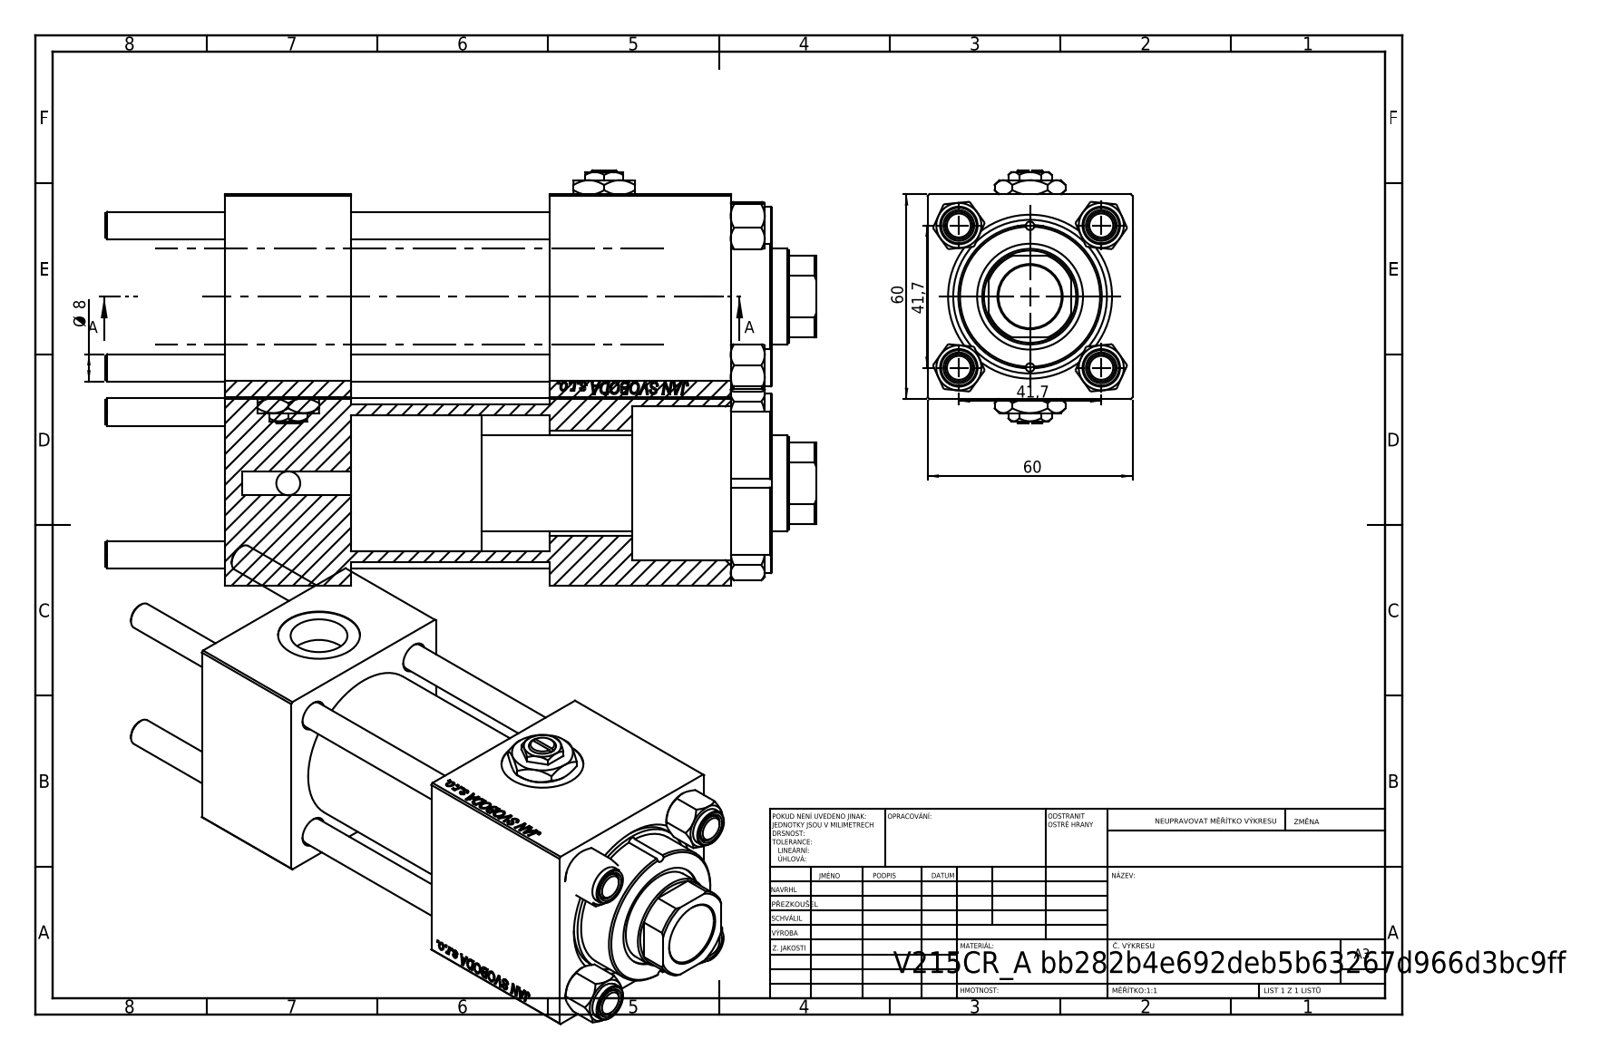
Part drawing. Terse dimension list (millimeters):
name: NUT_M5; V215CR_VCP; V215CR_BODY_A; CR025_012_A_0_G_A_G_M_020_+#_##_TYCINKA (+2 more)
written by: SolidWorks 2019 (CONFIG_CONTROL_DESIGN)
unit: mm
bodies: 13 solids, 1241 faces (571 planar, 92 cylindrical, 578 other)
size: 208 × 74 × 60
volume: 432 146 mm³; area: 123 152 mm²
holes: 4× ⌀8, 2× ⌀2.5, 2× ⌀7, 2× ⌀16.66, 2× ⌀24, 1× ⌀18.5, 1× ⌀28, 1× ⌀31, 1× ⌀40, 1× ⌀45
bosses: 4× ⌀11, 1× ⌀46, 1× ⌀42
rounds: 1× R13.5
face distances: 60, 37, 58, 95, 53, 148, 111, 119.3, 82.3, 24.3
hole spacings: 20.85, 29.49, 41.7, 46.53, 20.75, 58.97, 41.5, 92.5
